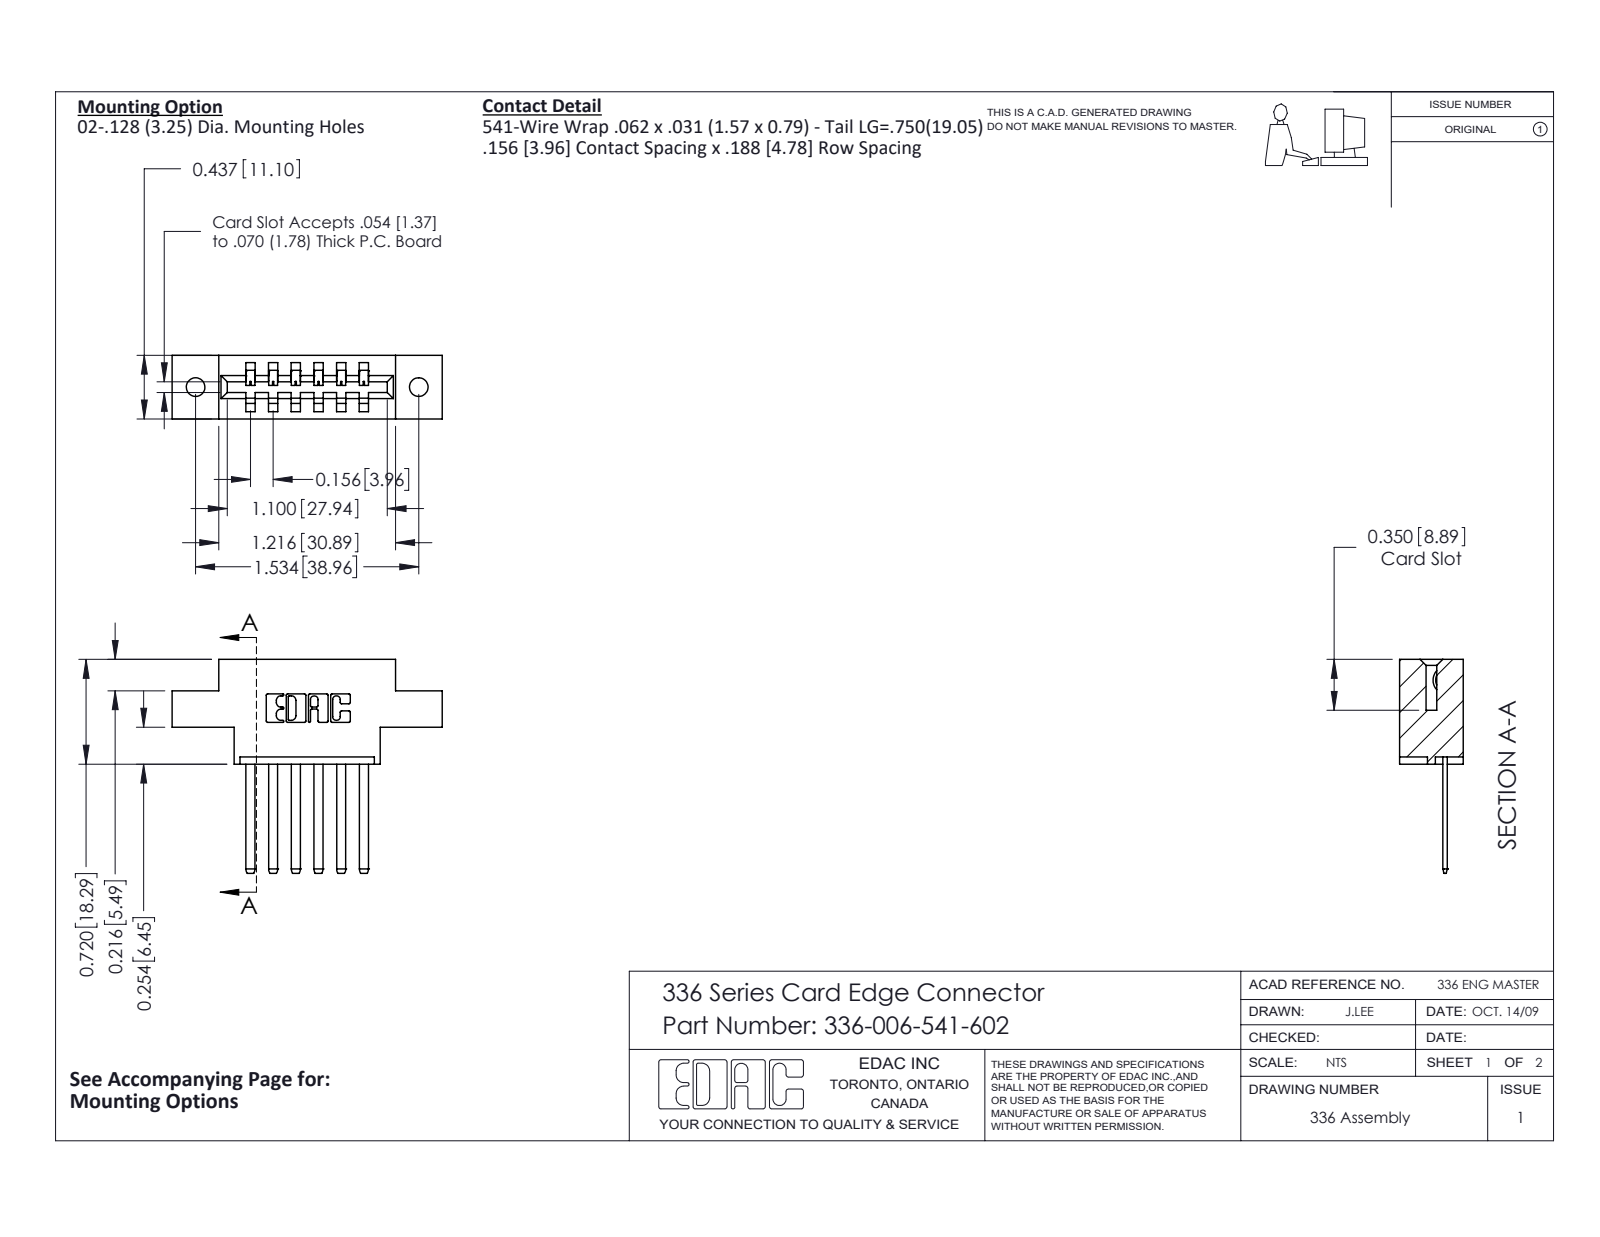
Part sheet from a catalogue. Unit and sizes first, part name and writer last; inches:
Units: inches
Overall size (bounding box): 1.857 × 1.47 × 0.437
Round holes (diameter × count): ⌀0.128 ×2
Partial cylindrical surfaces — rounded edges, fillets, slot ends (radius × count): R0.01 ×22, R0.004 ×12, R0.056 ×12, R0.007 ×6, R0.031 ×6, R0.026 ×3, R0.022 ×2, R0.04 ×2
Main face-to-face distances: 0.156, 0.437, 0.312, 0.376, 0.22, 0.181, 0.25, 0.256, 0.328, 0.109
Hole centre spacings: 1.534
Volume: 0.345 in³ · Surface area: 8.691 in²
Bodies: 7 solids, 418 faces (278 planar, 140 cylindrical, 0 other)
Part name (STEP PRODUCT): 336-290-001_336-290-541; 336-006-541-602; 336 Part_Offset - .128 Dia
STEP written by: SolidWorks 2020 (CONFIG_CONTROL_DESIGN)
